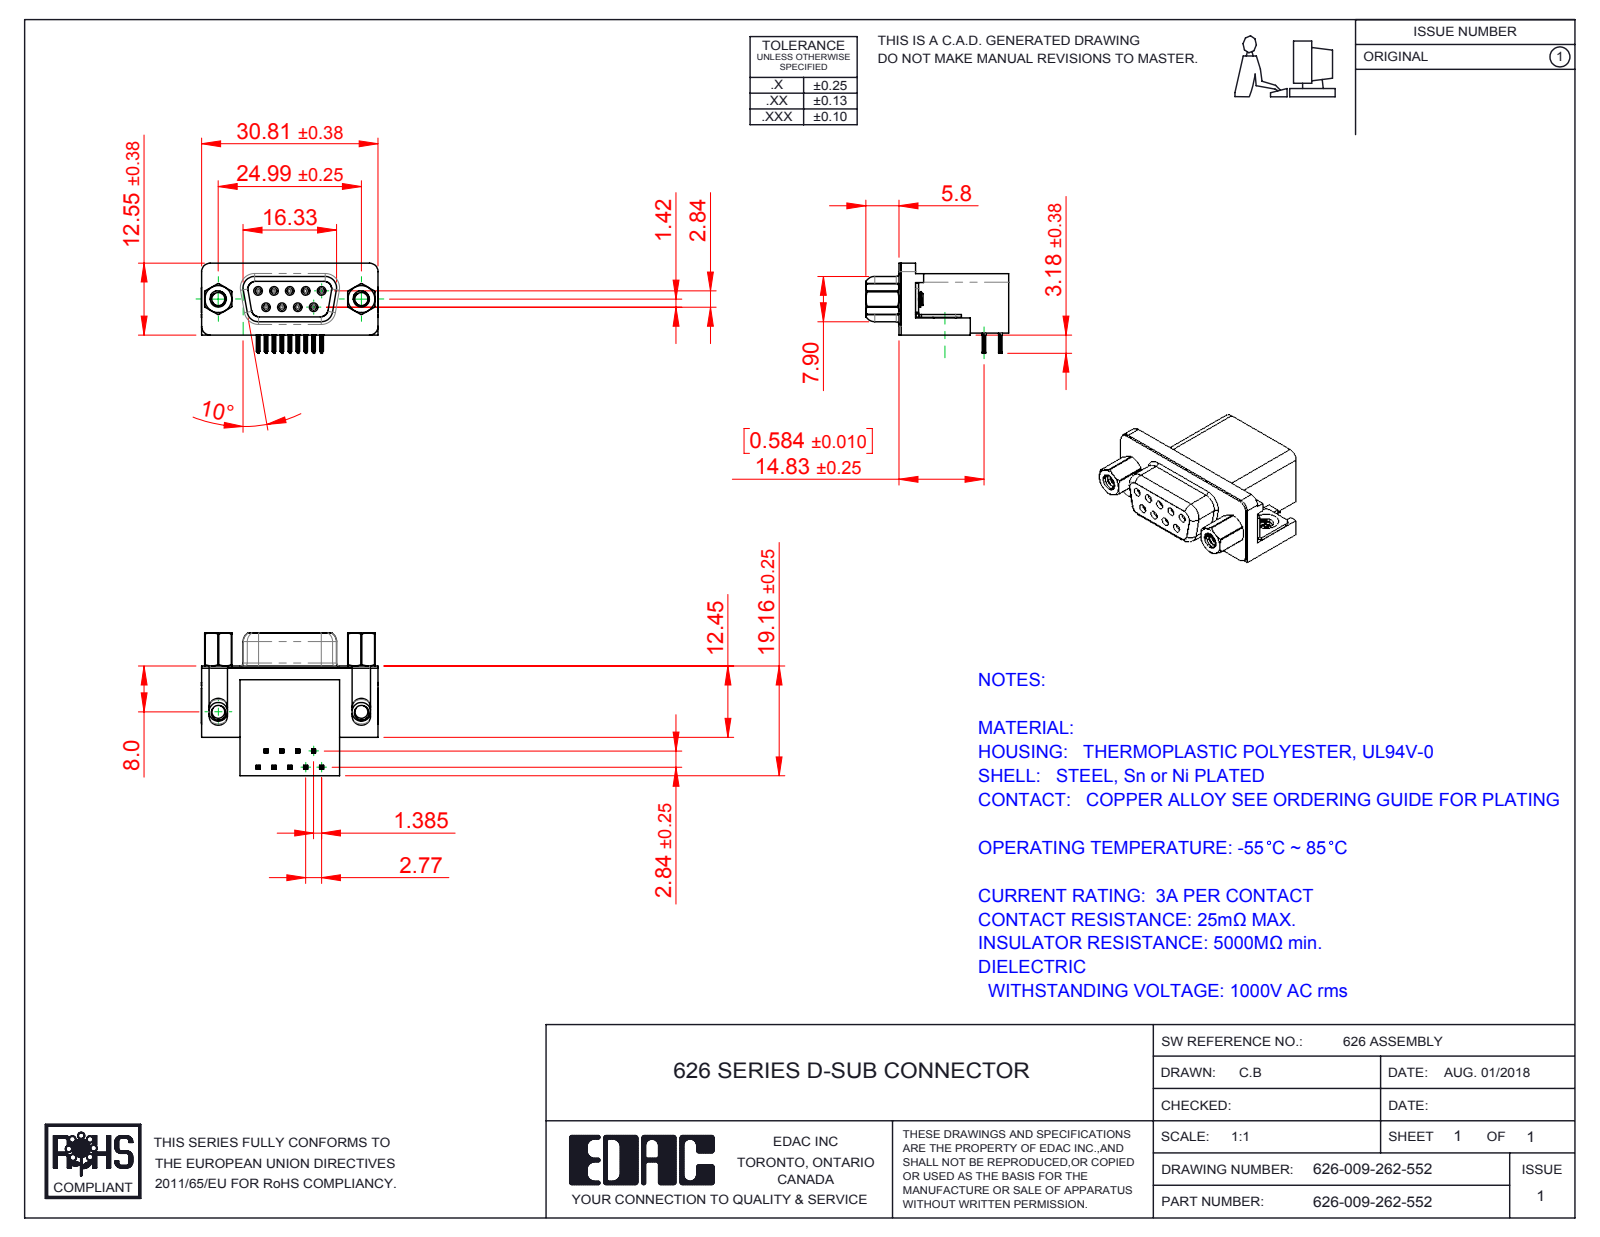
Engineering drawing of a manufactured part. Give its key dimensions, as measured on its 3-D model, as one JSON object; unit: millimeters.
{"part_name": "626 4-40 Hex Standoff 5; 626 Shell_9 Socket; 626 Housing_9 Socket; 626 Contact Top (+3 more)", "step_written_by": "SolidWorks 2016 (CONFIG_CONTROL_DESIGN)", "units": "millimeters", "bodies": {"solids": 15, "faces": 1642, "planar": 692, "cylindrical": 462, "other": 488}, "overall_size": [30.89, 24.96, 15.73], "volume_mm3": 5111, "surface_area_mm2": 6032, "round_holes": [[0.8, 9], [0.9, 9], [2.26, 2], [2.29, 2], [4, 2], [4.8, 2], [5, 2]], "round_bosses_or_shafts": [[1.2, 9], [4.9, 2], [3.26, 2], [2.79, 2]], "partial_cylinders_radius": [[0.1, 72], [0.15, 36], [0.35, 18], [1, 18], [0.34, 9], [1.35, 8], [1.6, 8], [1.5, 7]], "face_to_face_distances": [0.4, 10.34, 0.35, 18.76, 19.16, 16.26, 2.9, 2.5, 6.2, 5.8], "hole_center_spacings": [3.16, 2.77, 5.54, 5.03, 5.04, 8.31, 7.48, 7.49]}
